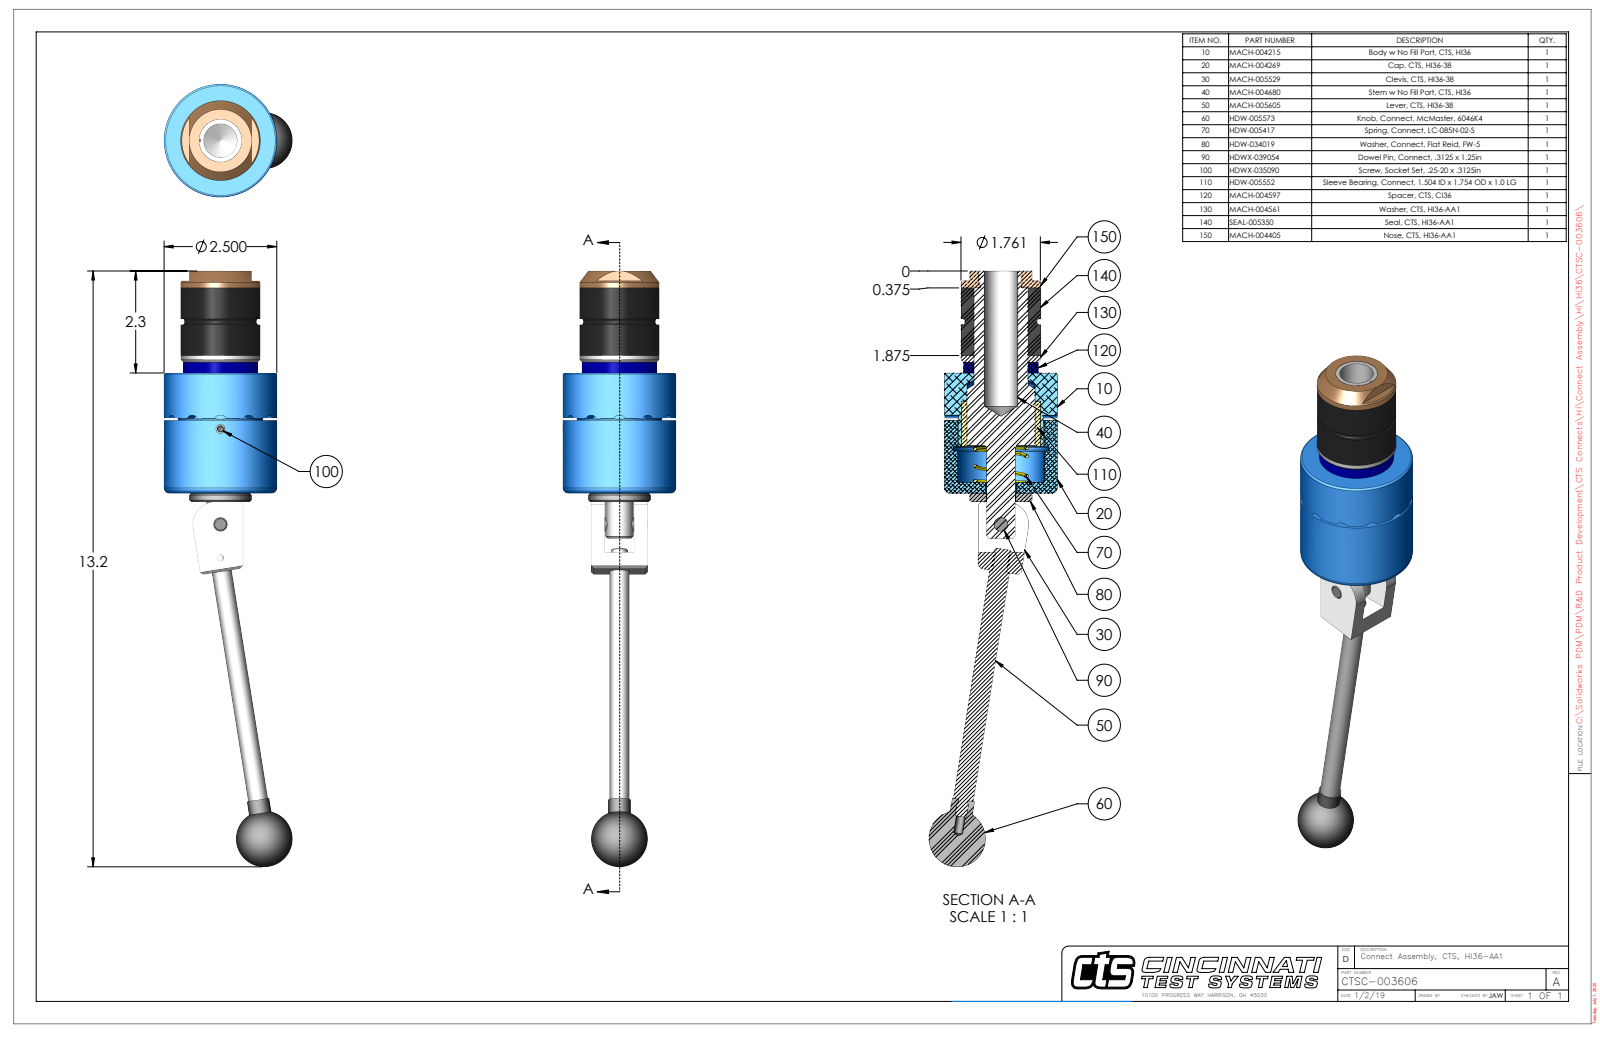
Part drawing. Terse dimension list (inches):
name: CTSC-003606
written by: SolidWorks 2023 (AUTOMOTIVE_DESIGN)
unit: in
bodies: 10 solids, 270 faces (97 planar, 106 cylindrical, 67 other)
size: 13.215 × 2.843 × 2.5
volume: 20.39 in³; area: 114.6 in²
holes: 2× ⌀0.201, 1× ⌀0.15, 1× ⌀0.311, 1× ⌀0.313, 1× ⌀0.314, 1× ⌀0.656, 1× ⌀0.696, 1× ⌀0.75, 1× ⌀0.922, 1× ⌀1.188, 1× ⌀1.19, 1× ⌀1.198
bosses: 1× ⌀2.5, 1× ⌀1.875, 1× ⌀1.761, 1× ⌀1.656, 1× ⌀1.38, 1× ⌀1.186, 1× ⌀1, 1× ⌀0.904
rounds: 12× R0.12, 2× R0.029, 1× R0.5, 1× R1.196
face distances: 2.668, 4.555, 1.887, 3.055, 0.387, 1.5, 2.905, 0.237, 0.15, 1.65
hole spacings: 0.74, 2.118, 2.858
